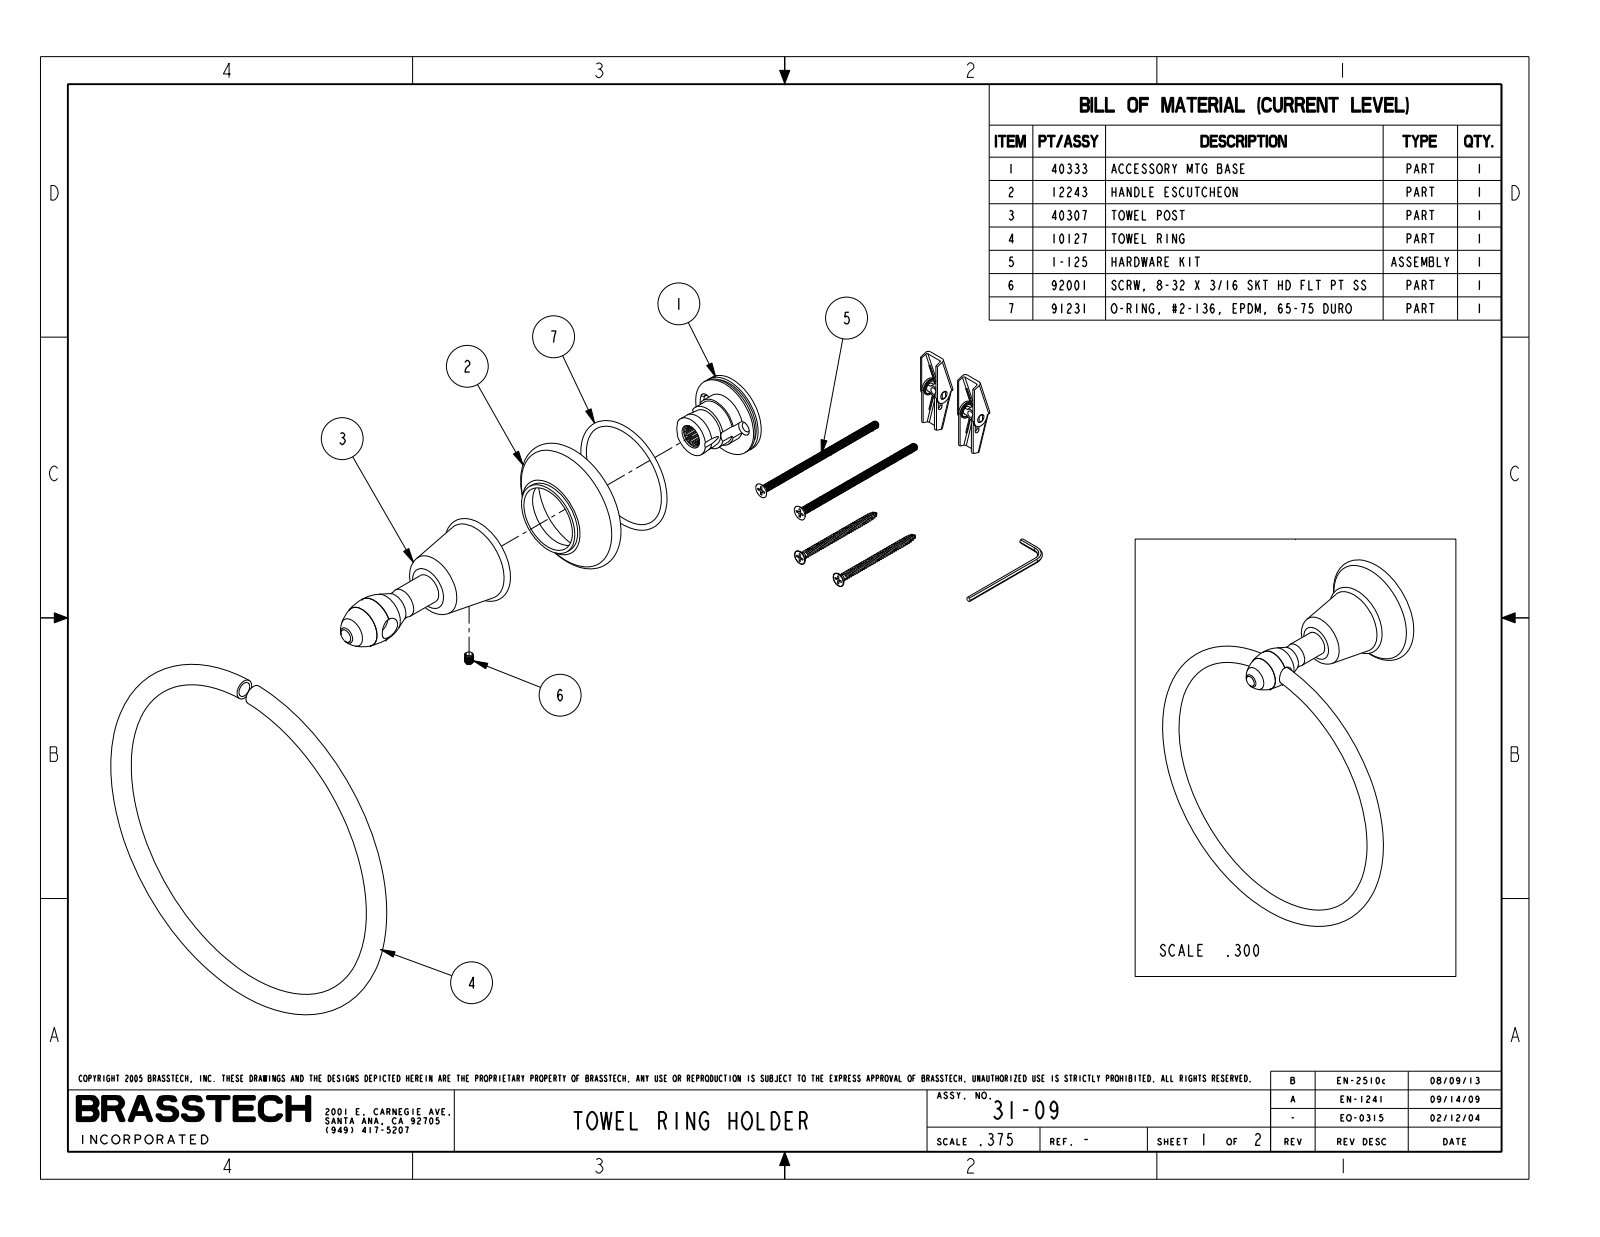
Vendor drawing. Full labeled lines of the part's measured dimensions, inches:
Part name (STEP PRODUCT): 31-09_WEB
STEP written by: PRO/ENGINEER BY PARAMETRIC TECHNOLOGY CORPORATION, 2009300 (CONFIG_CONTROL_DESIGN)
Units: inches
Bodies: 0 solids, 71 faces (4 planar, 26 cylindrical, 41 other)
Overall size (bounding box): 7.985 × 7 × 4.153
Round holes (diameter × count): ⌀0.136 ×1
Round bosses / shafts (diameter × count): ⌀0.553 ×1
Partial cylindrical surfaces — rounded edges, fillets, slot ends (radius × count): R0.203 ×1
Main face-to-face distances: 1.975
